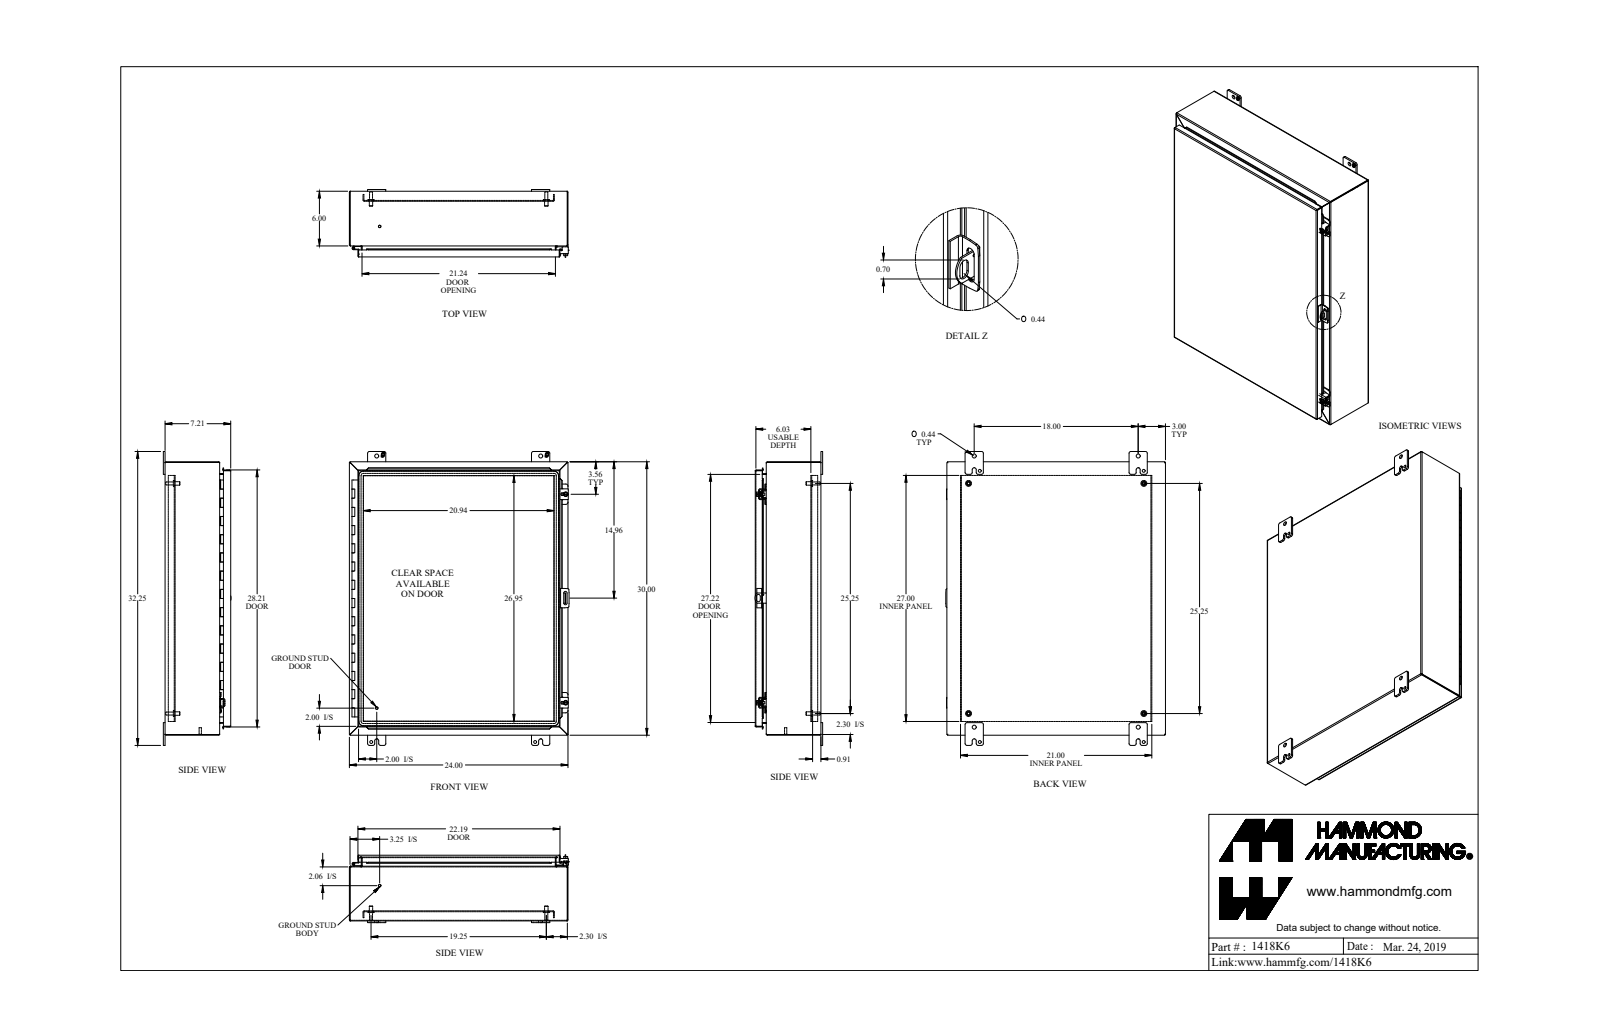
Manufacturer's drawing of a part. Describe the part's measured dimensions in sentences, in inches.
The part is named "1418K6". Its 3-D file was written by "SolidWorks 2019 (AUTOMOTIVE_DESIGN)". It is 38 solids with 1058 faces: 739 planar, 267 cylindrical and 52 other. Overall it measures 32.25 by 24.125 by 7.437 inches. Its volume is 248 cubic inches and its surface area 6 386 square inches. Round holes: 4 of diameter 0.313, 4 of diameter 0.437, 4 of diameter 0.5, 2 of diameter 0.213, 2 of diameter 0.265, 2 of diameter 0.307, 2 of diameter 0.375, 1 of diameter 0.125, 1 of diameter 0.187, 1 of diameter 0.445, 1 of diameter 0.445. Round bosses or shafts: 4 of diameter 0.65, 4 of diameter 0.375, 4 of diameter 0.33, 2 of diameter 1, 2 of diameter 0.5, 2 of diameter 0.39, 2 of diameter 0.281, 2 of diameter 0.25. Partial cylindrical surfaces (rounded edges, fillets, slot ends): 26 of radius 0.188, 24 of radius 0.036, 24 of radius 0.108, 13 of radius 0.048, 13 of radius 0.143, 8 of radius 0.045, 8 of radius 0.218, 8 of radius 0.25. The main face-to-face distances are 0.072, 7.113, 7.041, 7.185, 0.937, 0.095, 1.009, 6.081, 6.009, 1.032. The hole center spacings are 1.736, 18, 19.25, 29.75, 34.772, 33.837, 2.434, 3.065.
